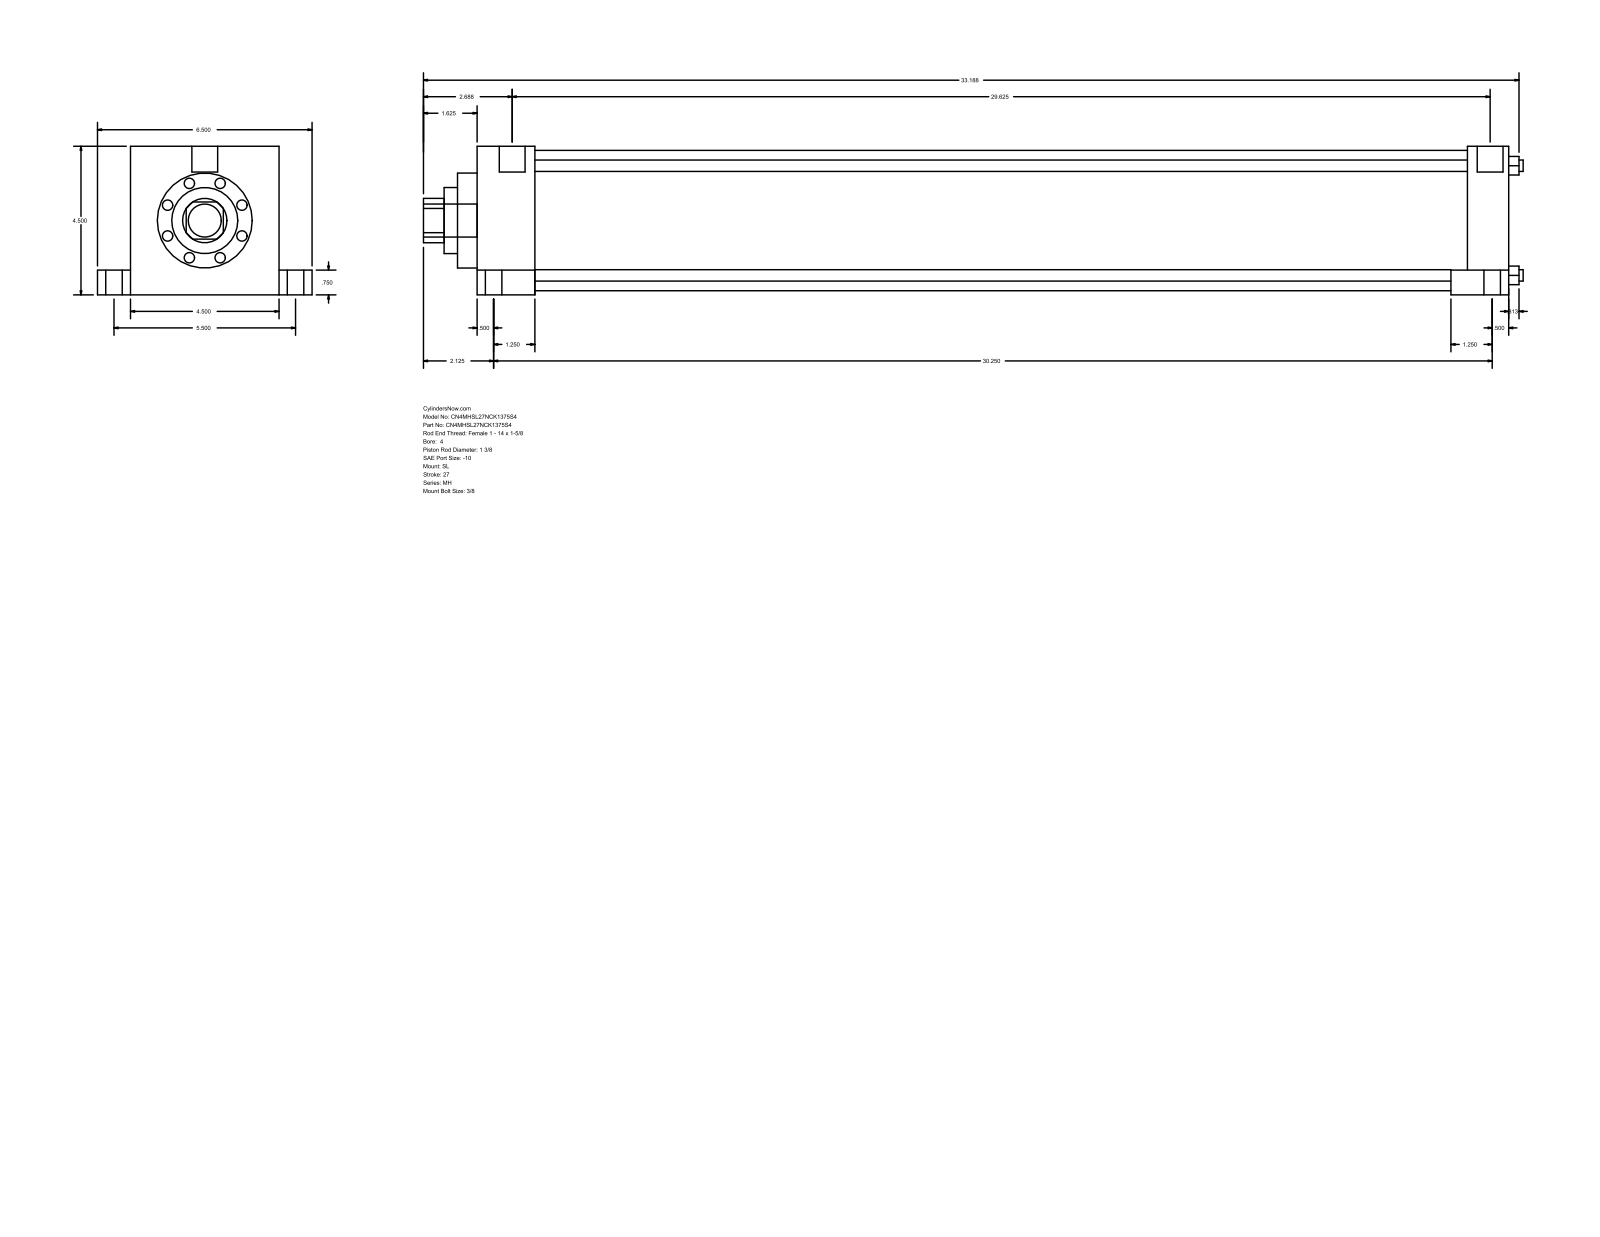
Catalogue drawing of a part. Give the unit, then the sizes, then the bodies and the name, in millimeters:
Units: millimetres
Overall size (bounding box): 846.14 × 165.1 × 114.3
Round holes (diameter × count): ⌀8.76 ×4, ⌀34.92 ×1, ⌀50.8 ×1, ⌀73.03 ×1, ⌀107.95 ×1
Round bosses / shafts (diameter × count): ⌀19.05 ×4, ⌀12.7 ×4, ⌀8.73 ×4, ⌀19.84 ×2, ⌀25.4 ×1
Partial cylindrical surfaces — rounded edges, fillets, slot ends (radius × count): R17.06 ×1
Main face-to-face distances: 114.3, 793.75, 44.45, 749.3, 762, 717.55, 31.75, 25.4, 139.7, 19.05
Hole centre spacings: 59.62, 84.32, 119.25
Bodies: 0 solids, 110 faces (77 planar, 33 cylindrical, 0 other)
Part name (STEP PRODUCT): MH_SL__0400_1.375
STEP written by: GSSL Pune (CONFIG_CONTROL_DESIGN)
